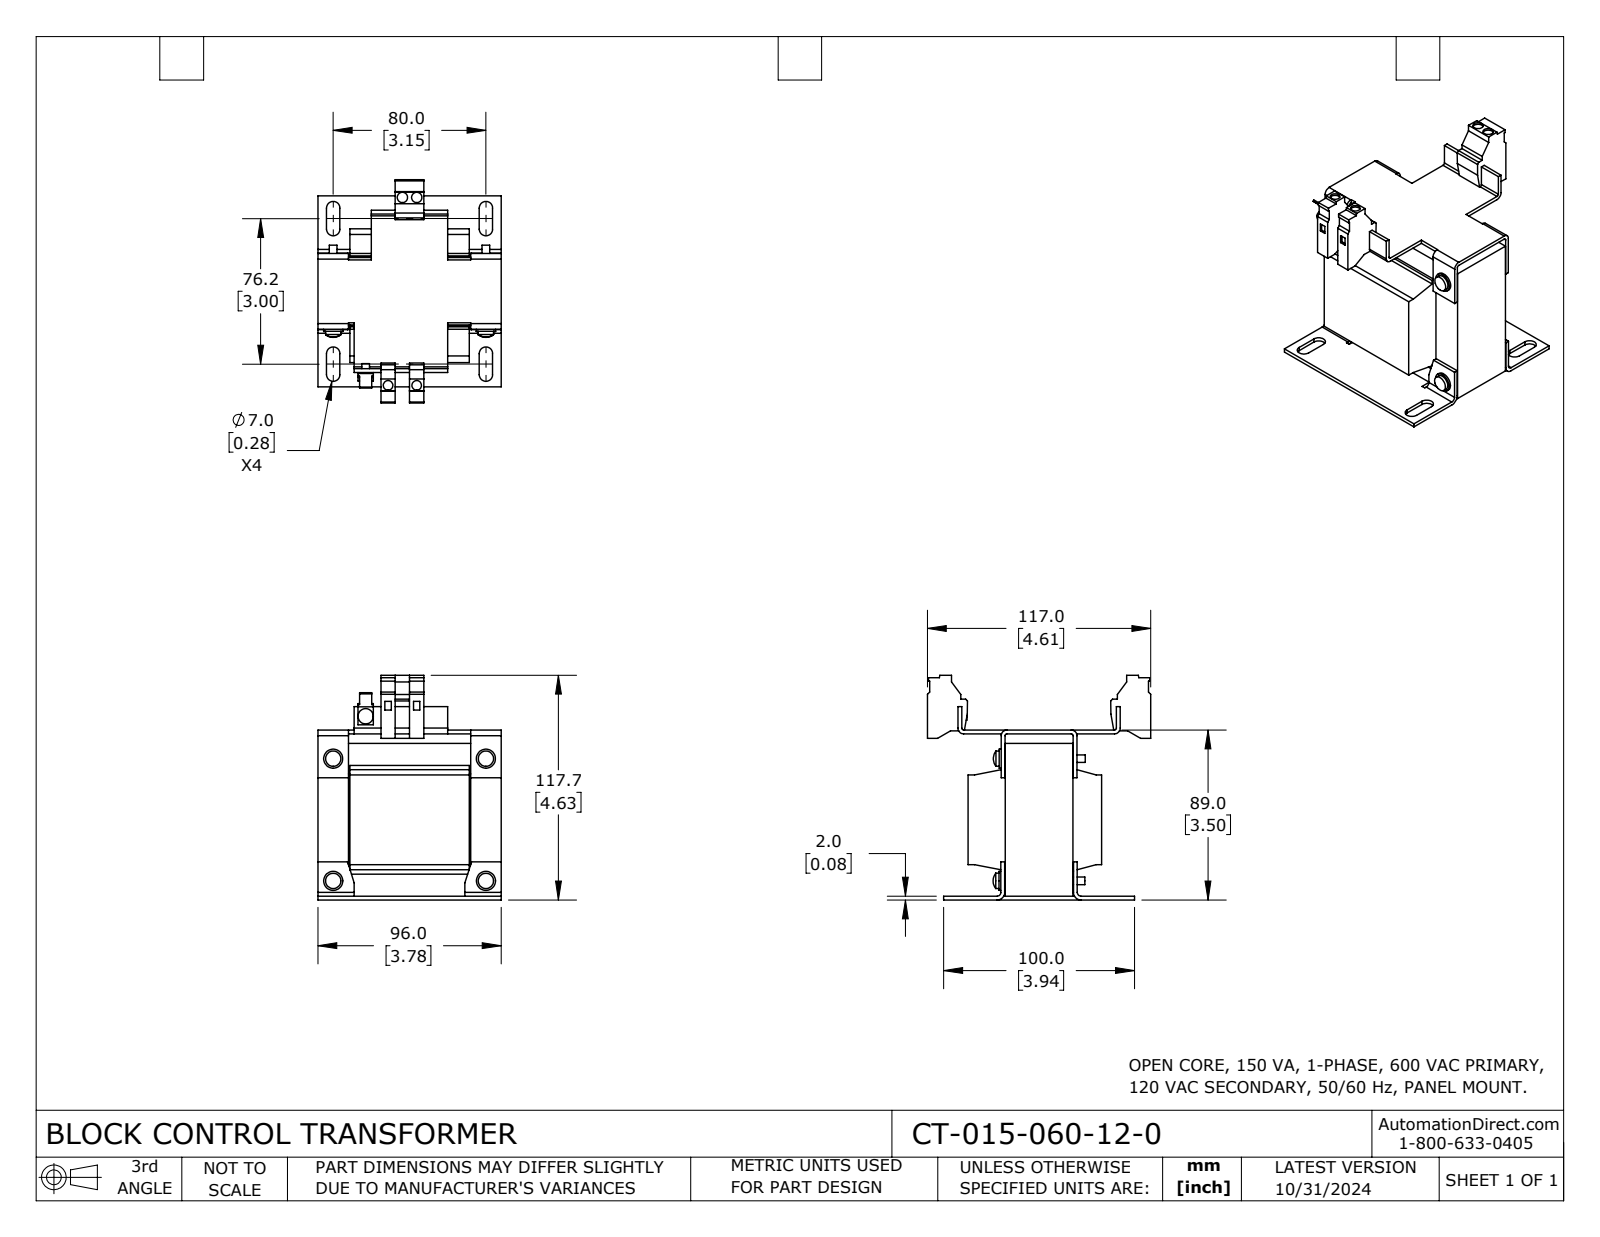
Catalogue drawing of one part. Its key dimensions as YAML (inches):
part_name: "CT-015-060-12-0"
step_written_by: "SolidWorks 2023 (CONFIG_CONTROL_DESIGN)"
units: inches
bodies: {solids: 1, faces: 334, planar: 245, cylindrical: 85, other: 4}
overall_size: [4.634, 4.606, 3.78]
volume: 26.09
surface_area: 135.1
round_holes:
  - {diameter: 0.197, count: 2}
  - {diameter: 0.213, count: 2}
round_bosses_or_shafts:
  - {diameter: 0.315, count: 5}
  - {diameter: 0.157, count: 5}
  - {diameter: 0.394, count: 4}
  - {diameter: 0.177, count: 4}
partial_cylinders:
  - {radius: 0.138, count: 8}
  - {radius: 0.039, count: 4}
  - {radius: 0.118, count: 4}
  - {radius: 0.079, count: 2}
  - {radius: 0.157, count: 2}
face_to_face_distances: [0.079, 3.425, 3.15, 0.63, 0.657, 3.122, 3.346, 3.504, 1.398, 2.52]
hole_center_spacings: [3.885, 0.295, 0.591, 3.874, 3.919]
